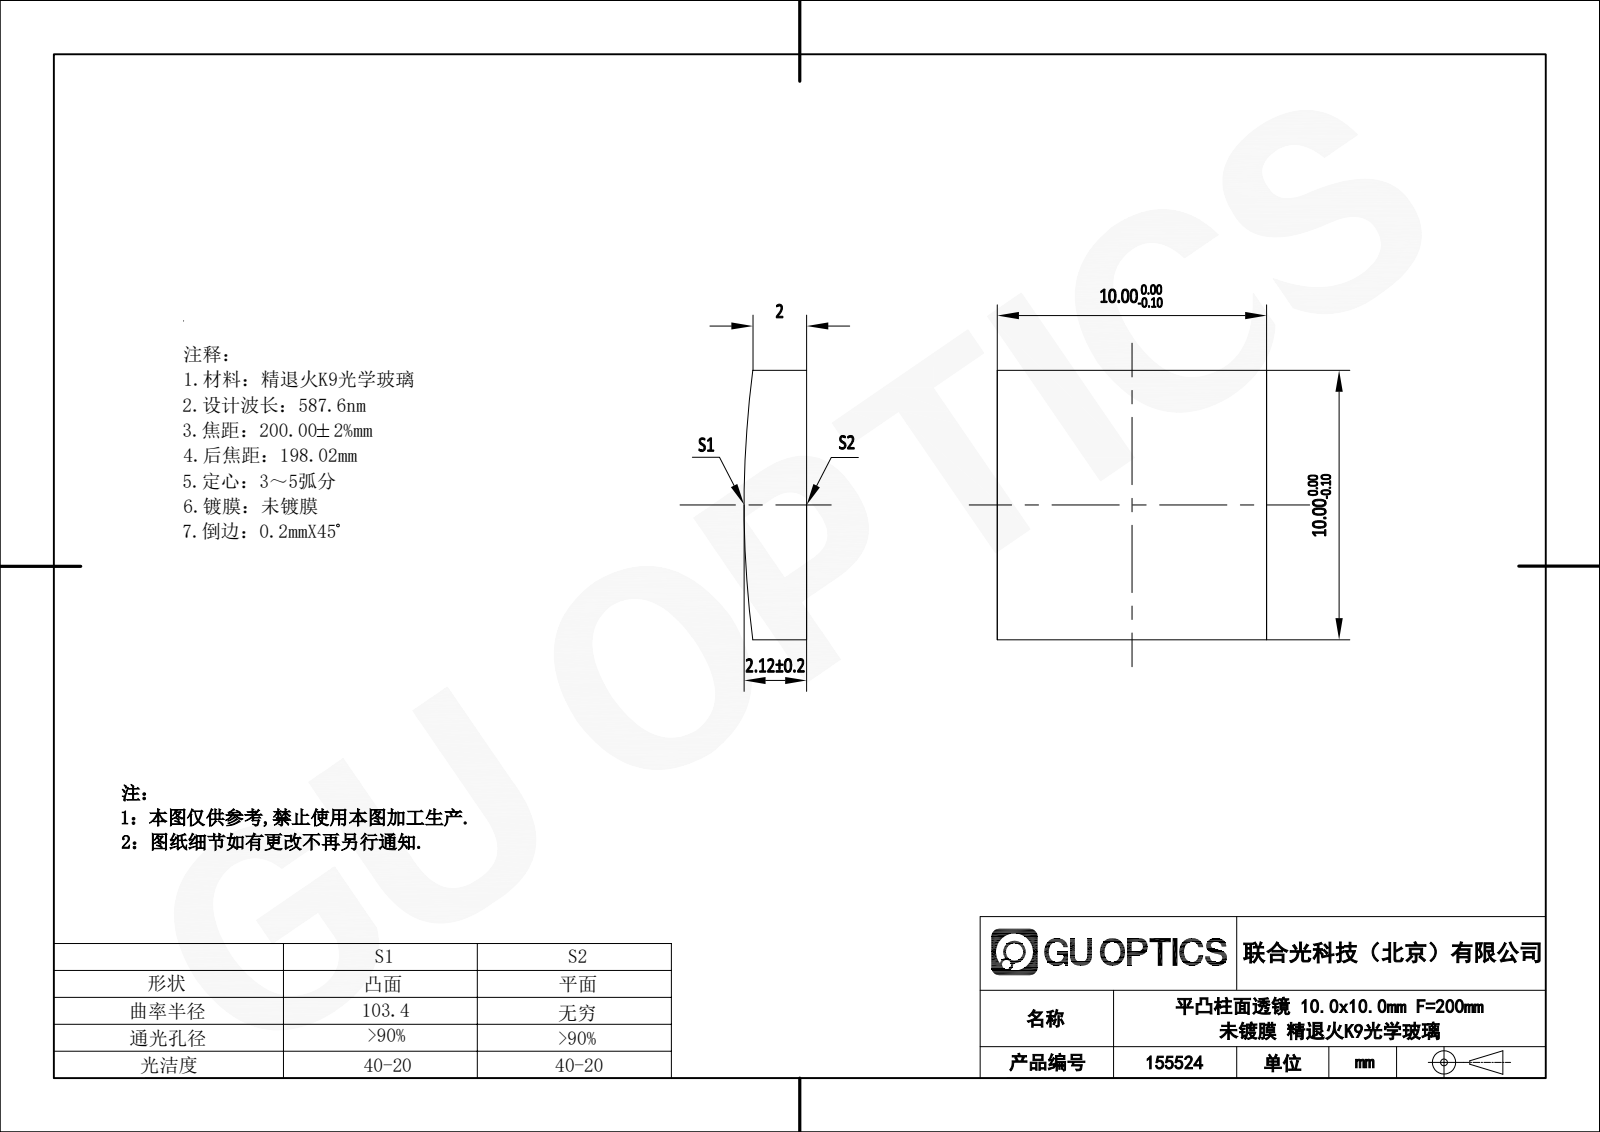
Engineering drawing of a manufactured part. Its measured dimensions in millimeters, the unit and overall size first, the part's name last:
Units: millimetres
Overall size (bounding box): 10 × 10 × 2.12
Partial cylindrical surfaces — rounded edges, fillets, slot ends (radius × count): R103.4 ×1
Main face-to-face distances: 10
Volume: 208 mm³ · Surface area: 282 mm²
Bodies: 1 solid, 7 faces (5 planar, 2 cylindrical, 0 other)
Part name (STEP PRODUCT): 155524
STEP written by: SolidWorks 2020 (CONFIG_CONTROL_DESIGN)
